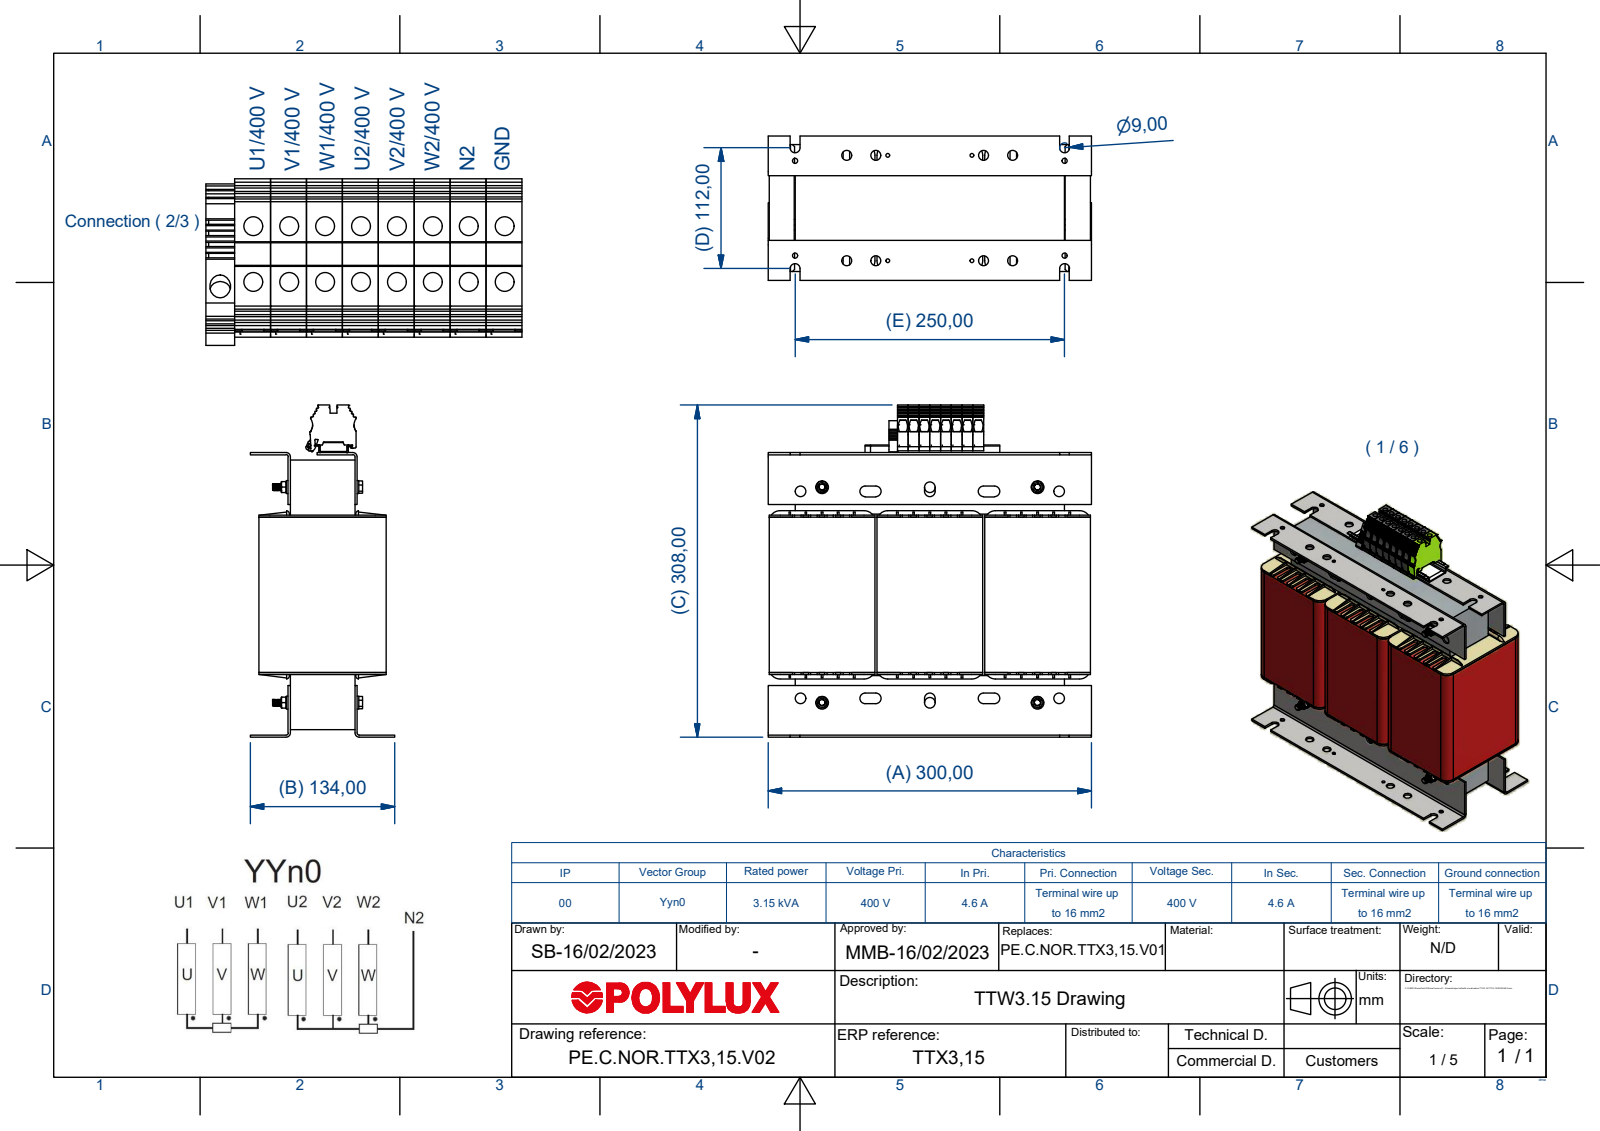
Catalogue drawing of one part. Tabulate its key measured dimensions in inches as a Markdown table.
| quantity | value |
| --- | --- |
| part name | TTX3.15; Núcleo RC50x60; BRI50-3IP0E25; DIN 934 - M6 x 1 (+8 more) |
| STEP written by | Autodesk Inventor 2018 (AUTOMOTIVE_DESIGN) |
| units | inches |
| bodies | 39 solids, 2694 faces (1912 planar, 734 cylindrical, 48 other) |
| overall size | 12.13 × 11.811 × 5.276 |
| volume | 416.7 in³ |
| surface area | 1 755 in² |
| round holes (diameter × count) | 0.209 × 16, 0.354 × 12, 0.194 × 10, 0.394 × 10, 0.138 × 6, 0.252 × 4, 0.118 × 2, 0.228 × 2 |
| round bosses / shafts (diameter × count) | 0.472 × 4, 0.236 × 4 |
| partial cylindrical surfaces (radius × count) | 0.02 × 33, 0.118 × 28, 0.433 × 18, 0.039 × 16, 0.394 × 16, 0.012 × 10, 0.197 × 10, 0.004 × 9 |
| main face-to-face distances | 0.079, 3.937, 2.441, 2.992, 2.362, 0.049, 7.874, 0.866, 0.945, 6.929 |
| hole center spacings | 2.441, 3.937, 0.433, 1.063, 1.417, 1.496, 1.9, 2.959 |
